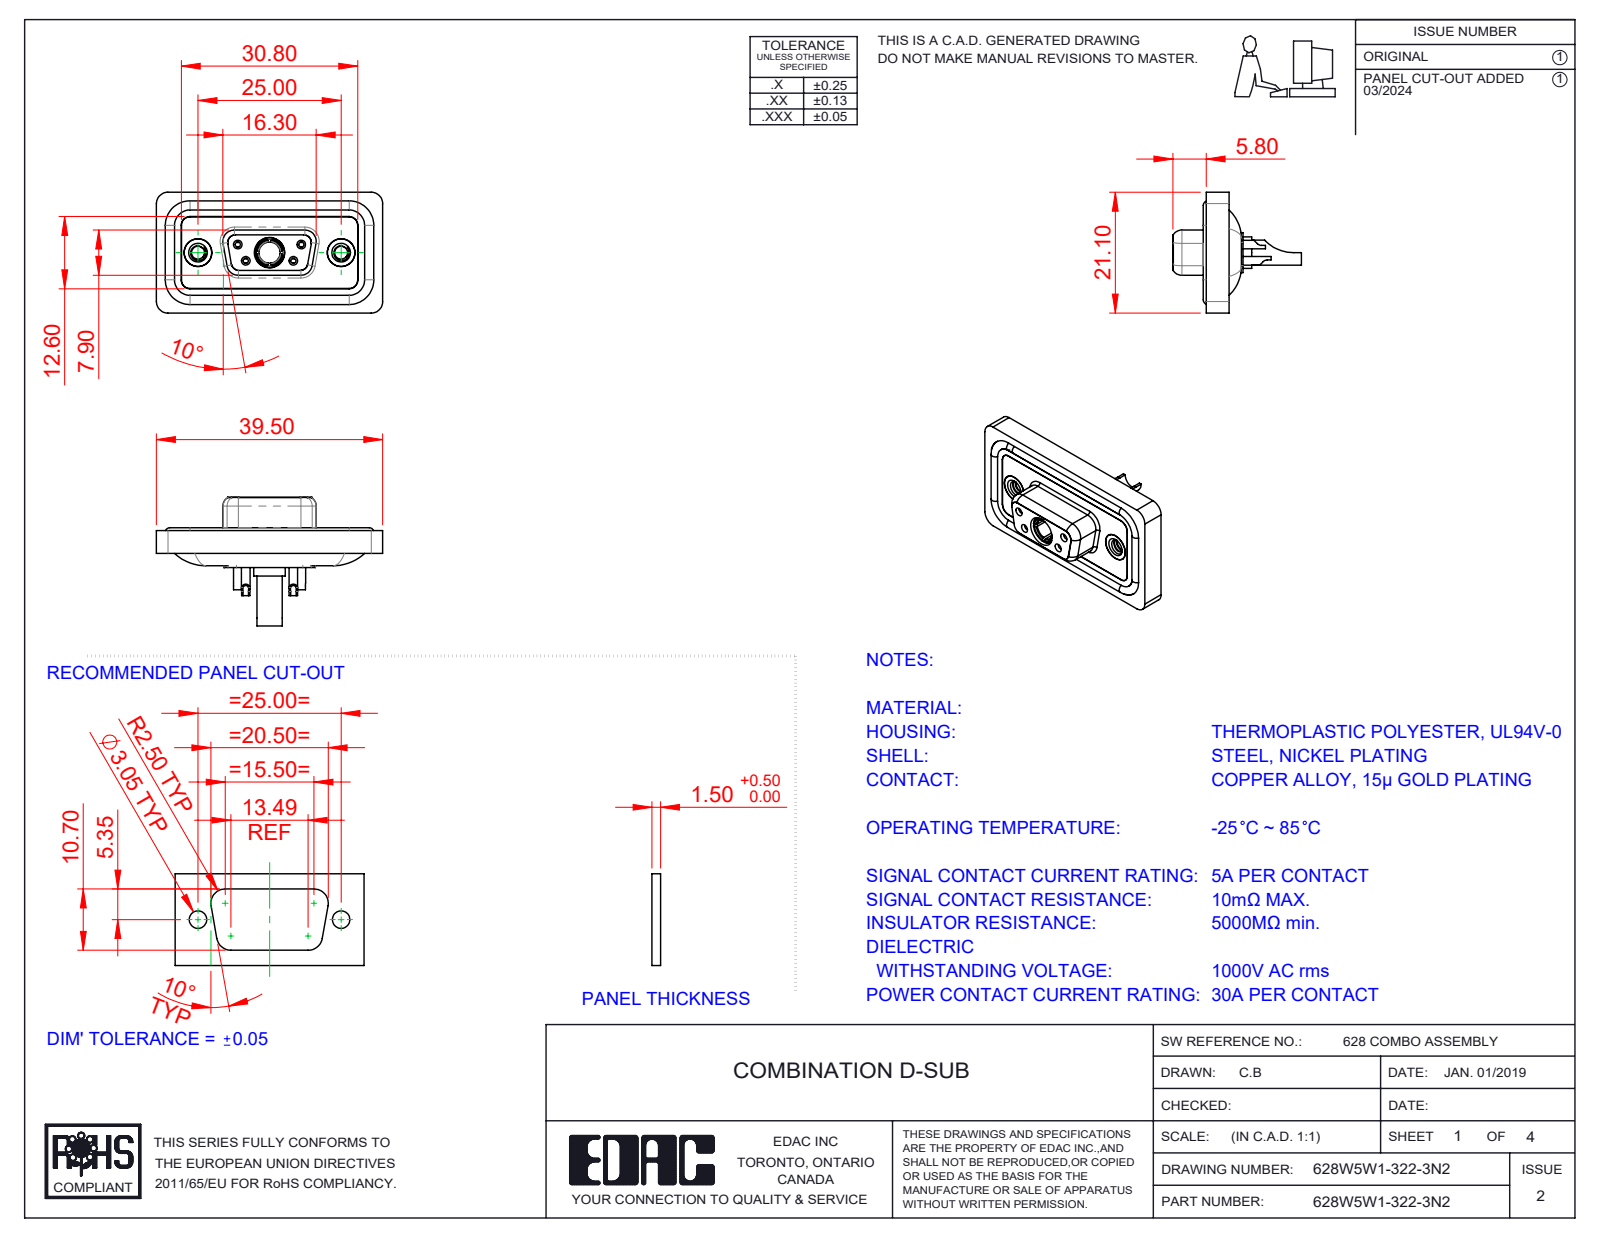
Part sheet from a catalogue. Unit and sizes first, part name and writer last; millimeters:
Units: millimetres
Overall size (bounding box): 39.5 × 22.45 × 21.1
Round holes (diameter × count): ⌀0.9 ×4, ⌀1 ×4, ⌀1.1 ×4, ⌀1.5 ×4, ⌀2 ×4, ⌀4.85 ×3, ⌀1.6 ×2, ⌀1.7 ×2, ⌀2.26 ×2, ⌀4 ×2, ⌀4.05 ×2, ⌀5 ×2
Round bosses / shafts (diameter × count): ⌀1.6 ×6, ⌀2.2 ×4, ⌀4.95 ×2, ⌀4.8 ×2, ⌀5.5 ×1, ⌀5.2 ×1, ⌀4.96 ×1, ⌀4.75 ×1
Partial cylindrical surfaces — rounded edges, fillets, slot ends (radius × count): R1.5 ×22, R2 ×18, R1.35 ×8, R1.6 ×8, R1 ×6, R0.25 ×4, R0.5 ×4, R0.6 ×4
Main face-to-face distances: 0.4, 2.9, 1.1, 1.8, 1.6, 0.5, 5.65, 7.45, 5.35, 3.6
Hole centre spacings: 3.16, 5.72, 7.1, 12.5, 18.1, 4.39, 4.4, 8.31
Volume: 4 799 mm³ · Surface area: 7 785 mm²
Bodies: 13 solids, 686 faces (205 planar, 298 cylindrical, 183 other)
Part name (STEP PRODUCT): 628Combo Shell Front_09 Contacts; 628Combo Shell Rear_09 Contacts; 628Combo Waterproof Housing_09 Contacts; 628Combo Housing_5W1 (+5 more)
STEP written by: SolidWorks 2023 (CONFIG_CONTROL_DESIGN)
